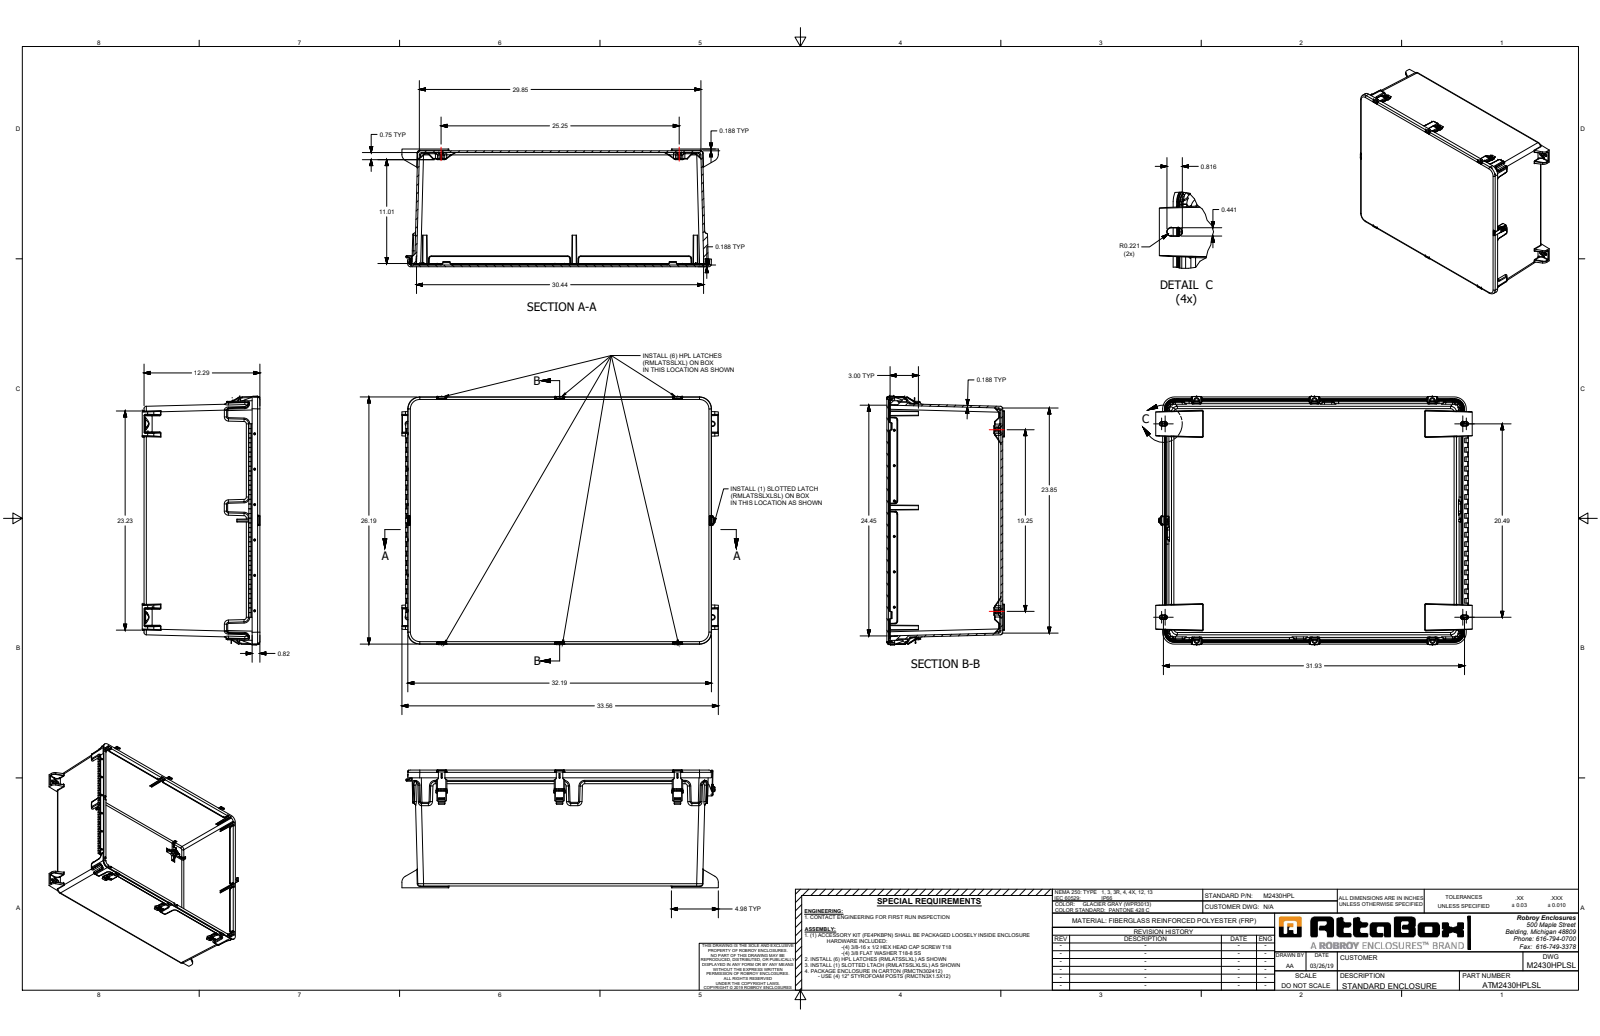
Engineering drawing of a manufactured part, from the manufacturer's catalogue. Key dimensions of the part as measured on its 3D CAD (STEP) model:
Part name (STEP PRODUCT): M2430HPLSL
STEP written by: SolidWorks 2019 (AUTOMOTIVE_DESIGN)
Units: inches
Bodies: 52 solids, 4150 faces (1264 planar, 1513 cylindrical, 1373 other)
Overall size (bounding box): 33.556 × 26.359 × 12.568
Volume: 612 in³ · Surface area: 6 388 in²
Round holes (diameter × count): ⌀0.195 ×12, ⌀0.196 ×12, ⌀0.089 ×6, ⌀0.075 ×4, ⌀0.135 ×4, ⌀0.309 ×4, ⌀0.375 ×4, ⌀0.135 ×3, ⌀0.075 ×2, ⌀0.375 ×2, ⌀0.098 ×1, ⌀0.12 ×1
Round bosses / shafts (diameter × count): ⌀0.125 ×8, ⌀0.5 ×4, ⌀0.125 ×4, ⌀0.3 ×2, ⌀0.594 ×1, ⌀0.524 ×1, ⌀0.24 ×1, ⌀0.092 ×1
Partial cylindrical surfaces — rounded edges, fillets, slot ends (radius × count): R0.05 ×125, R0.02 ×106, R0.063 ×100, R0.005 ×84, R0.125 ×58, R0.25 ×58, R0.015 ×48, R0.03 ×48
Main face-to-face distances: 0.188, 12.098, 0.188, 12.286, 11.909, 0.439, 0.294, 0.482, 0.154, 0.145
Hole centre spacings: 3.75, 7.5, 0.439, 11.25, 3.384, 4.13, 7.13, 7.877
